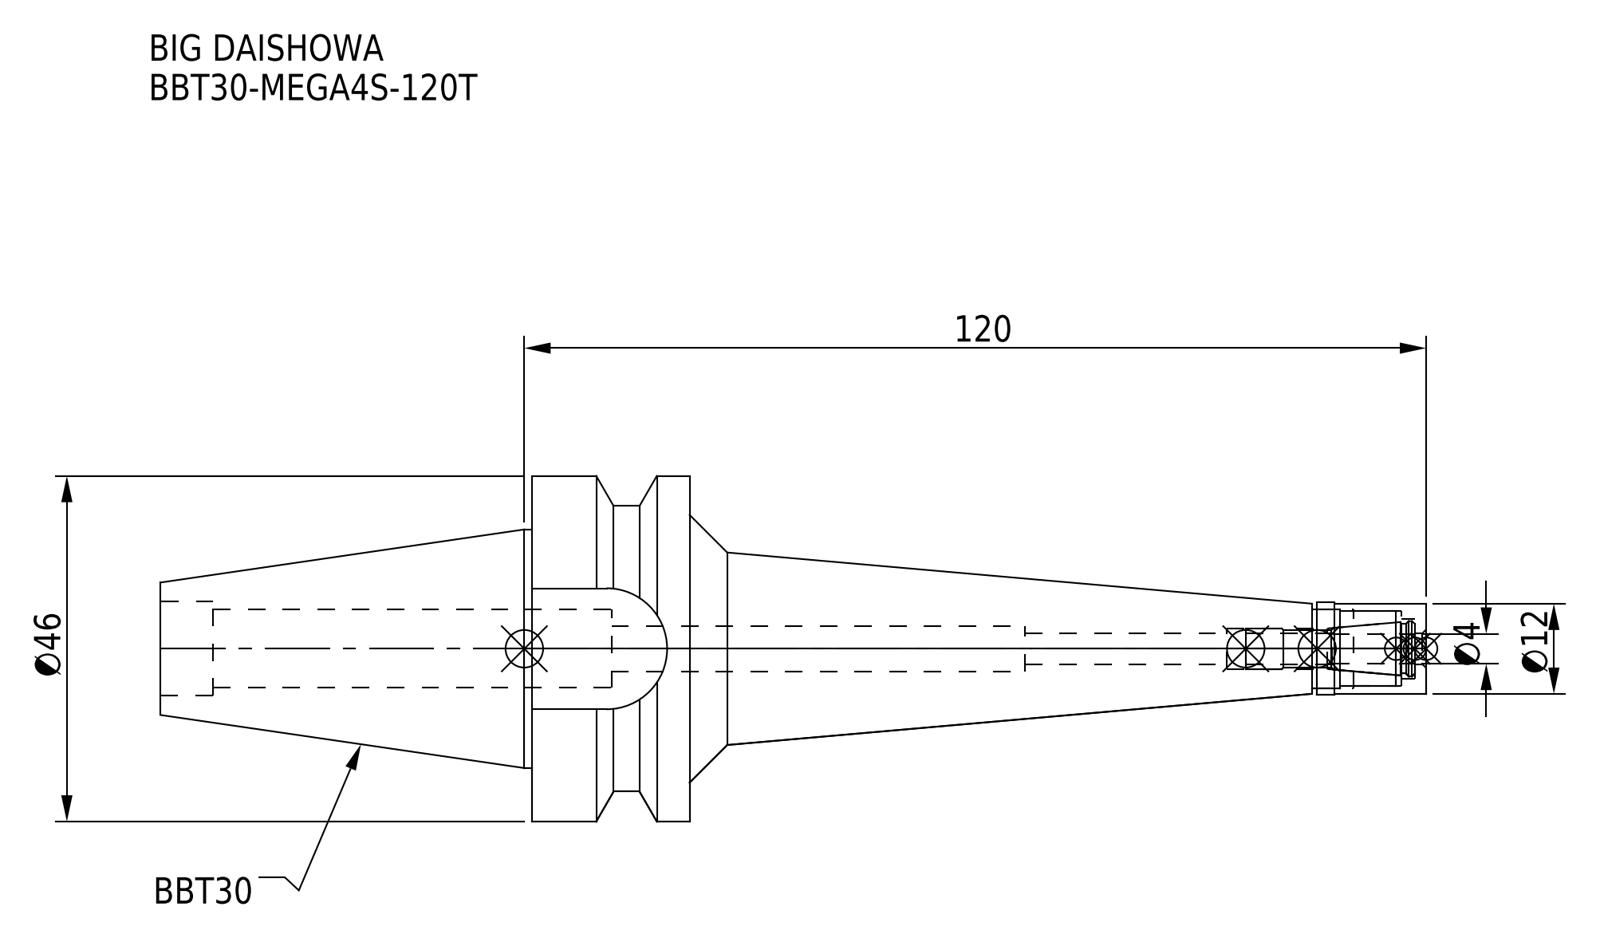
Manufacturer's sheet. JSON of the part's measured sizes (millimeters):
{"part_name": "BBT30-MEGA4S-120T; MGN4S_1.stp; BBT30-MEGA4S-120T_1.stp; DXF_TEMP_ASSY_ASM_4_ASM.stp (+3 more)", "step_written_by": "SolidWorks 2019 (CONFIG_CONTROL_DESIGN)", "units": "millimeters", "bodies": {"solids": 2, "faces": 74, "planar": 22, "cylindrical": 38, "other": 14}, "overall_size": [168.4, 46, 46], "volume_mm3": 73758, "surface_area_mm2": 19939, "round_holes": [[4.1, 1], [4.2, 1], [5.4, 1], [6, 1], [8, 1], [10, 1], [10.4, 1], [10.5, 1], [12.5, 1]], "round_bosses_or_shafts": [[46, 1], [31.75, 1], [12.3, 1], [12, 1]], "partial_cylinders_radius": [[8.05, 1], [19, 1]], "face_to_face_distances": [21, 32.6, 49.4, 70.4, 16.1, 98, 119, 168.4, 0.7, 108.4]}
